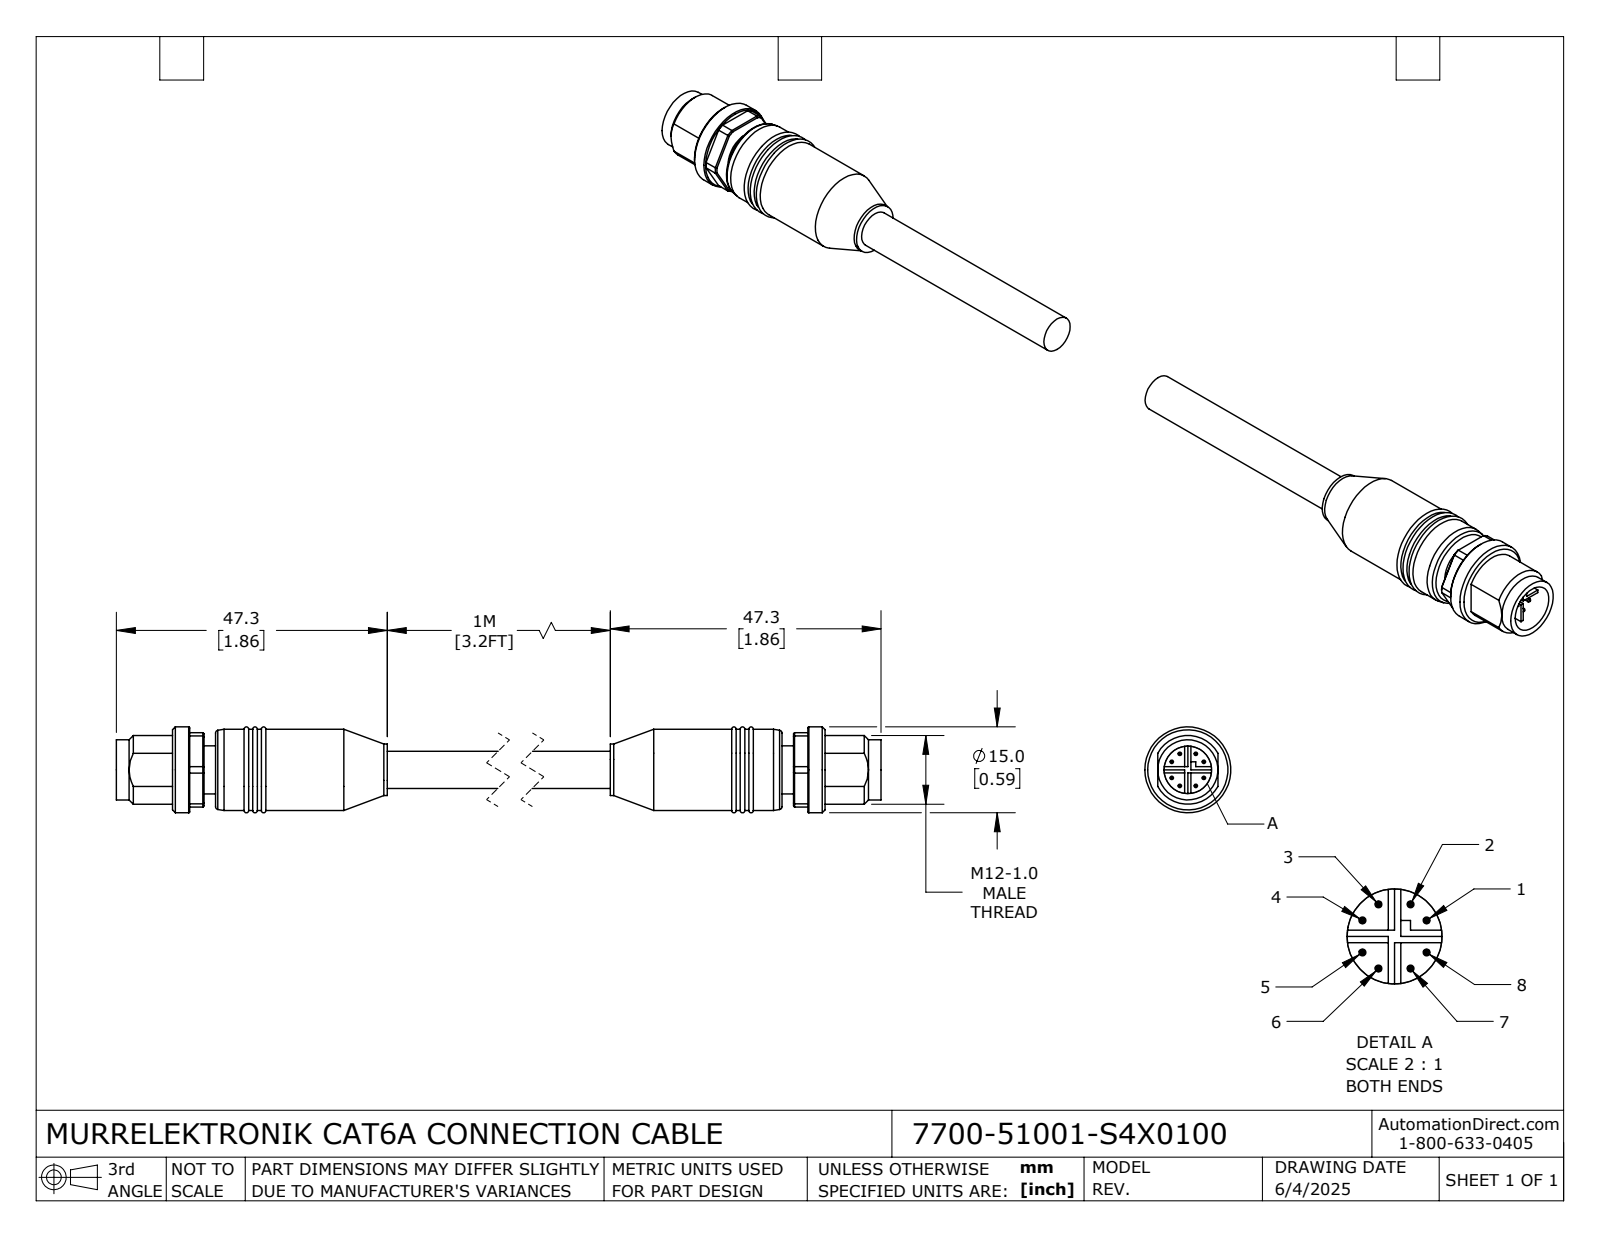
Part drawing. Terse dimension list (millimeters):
name: 7700-51001-S4X0100_MALE; 7700-51001-S4X0100
written by: SolidWorks 2024 (CONFIG_CONTROL_DESIGN)
unit: mm
bodies: 2 solids, 282 faces (112 planar, 88 cylindrical, 82 other)
size: 209.6 × 15 × 15
volume: 14 953 mm³; area: 7 635 mm²
holes: 1× ⌀8.3
bosses: 8× ⌀0.6, 1× ⌀15, 1× ⌀14.2, 1× ⌀10.5, 1× ⌀9, 1× ⌀8.4, 1× ⌀6.5
rounds: 1× R6, 1× R7.2
face distances: 4.7, 5.8, 2, 177, 1.1, 5.5, 13, 7.5, 182.5, 184.5
